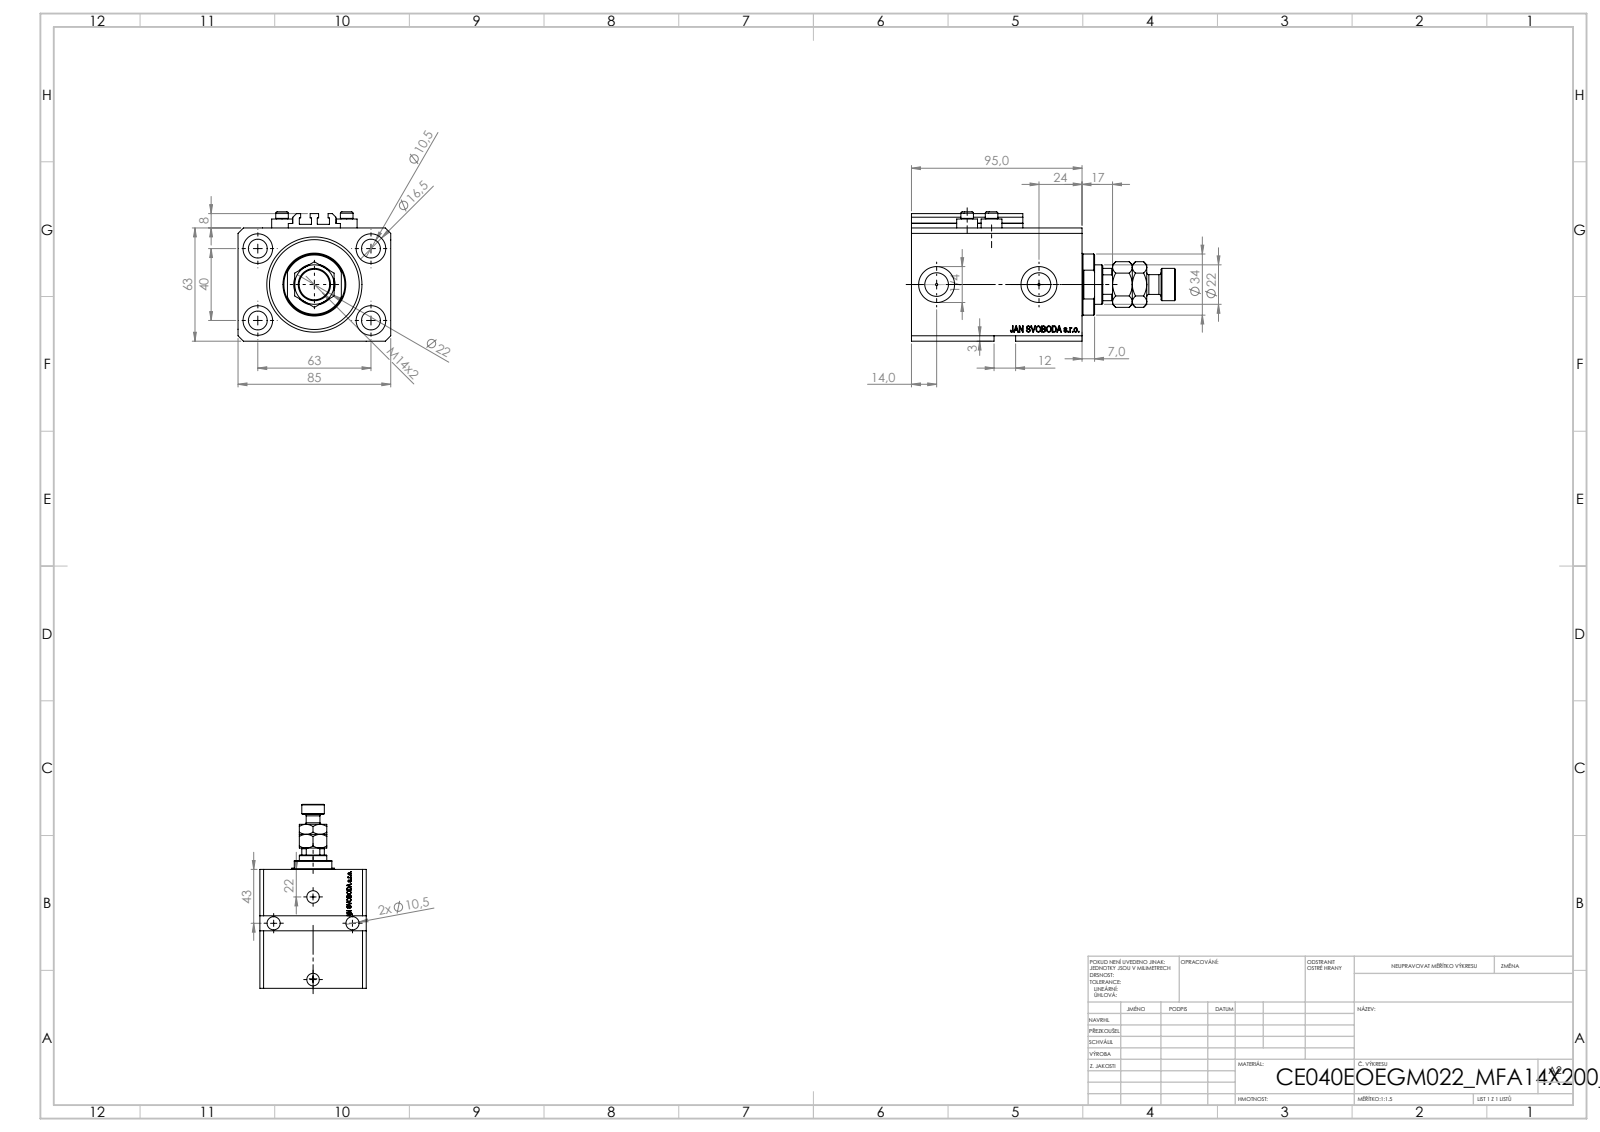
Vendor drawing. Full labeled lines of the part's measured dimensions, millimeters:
Part name (STEP PRODUCT): ALLEN BOLT V250CE; V250CE_E_Body; V250CE_VC_E; MFA (+1 more)
STEP written by: SolidWorks 2019 (CONFIG_CONTROL_DESIGN)
Units: millimetres
Bodies: 9 solids, 1139 faces (551 planar, 130 cylindrical, 458 other)
Overall size (bounding box): 147 × 85 × 72
Volume: 456 422 mm³ · Surface area: 100 450 mm²
Round holes (diameter × count): ⌀10.5 ×6, ⌀1.25 ×4, ⌀4 ×4, ⌀16.5 ×4, ⌀10 ×2, ⌀13.16 ×2, ⌀20 ×2, ⌀12.5 ×1, ⌀22 ×1, ⌀40 ×1, ⌀53 ×1
Round bosses / shafts (diameter × count): ⌀11.6 ×4, ⌀7 ×4, ⌀34 ×1, ⌀18 ×1, ⌀11 ×1
Partial cylindrical surfaces — rounded edges, fillets, slot ends (radius × count): R0.2 ×10, R10.5 ×1
Main face-to-face distances: 63, 85, 17, 95, 78, 11.4, 66.6, 83.6, 3, 22
Hole centre spacings: 37.31, 63, 13.6, 15.4, 24.96, 29.58, 30, 33.62
